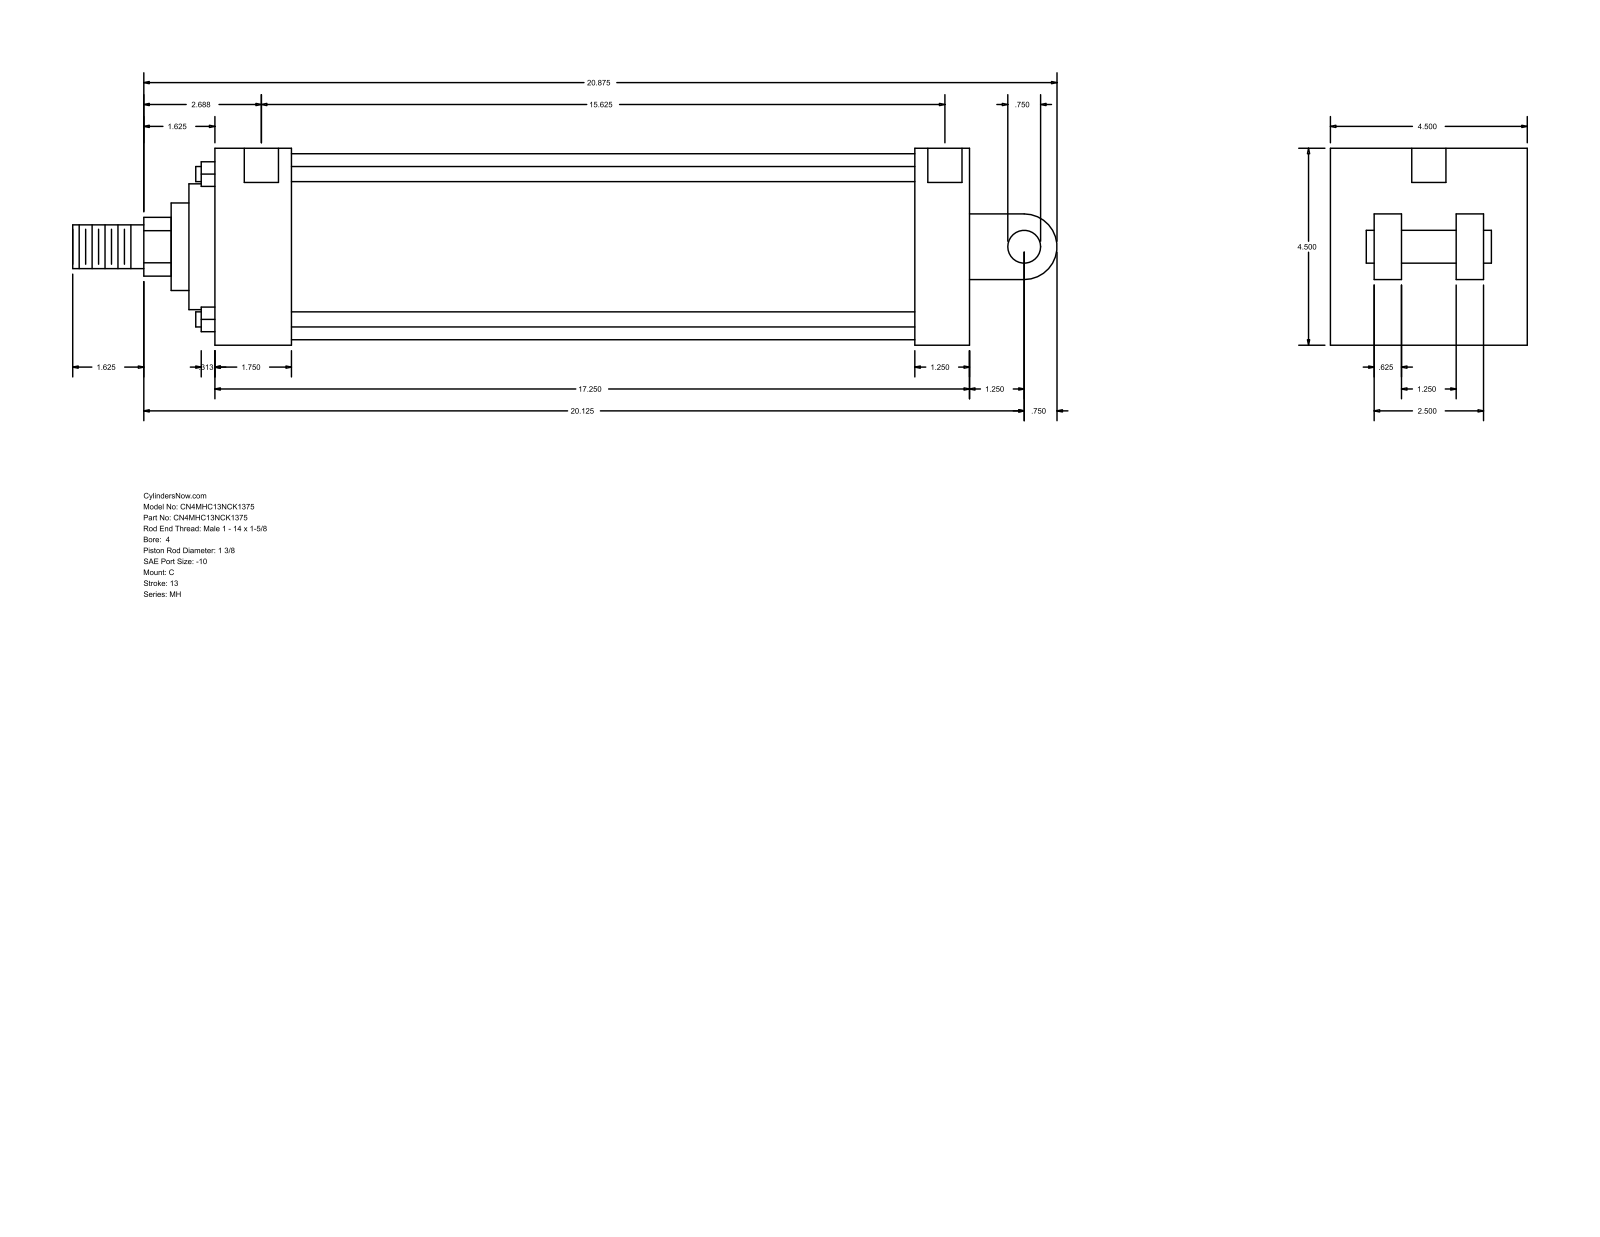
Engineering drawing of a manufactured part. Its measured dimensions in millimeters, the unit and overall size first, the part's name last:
Units: millimetres
Overall size (bounding box): 571.5 × 114.3 × 114.3
Round holes (diameter × count): ⌀8.73 ×4, ⌀19.84 ×2
Round bosses / shafts (diameter × count): ⌀8.76 ×4, ⌀107.95 ×1, ⌀73.03 ×1, ⌀50.8 ×1, ⌀34.92 ×1, ⌀25.4 ×1, ⌀19.05 ×1
Partial cylindrical surfaces — rounded edges, fillets, slot ends (radius × count): R17.06 ×1, R19.05 ×1
Main face-to-face distances: 114.3, 438.16, 44.45, 406.41, 361.96, 393.71, 31.75, 41.27, 73.03, 38.1
Hole centre spacings: 1.59, 398.47, 400.06, 396.88
Bodies: 0 solids, 101 faces (71 planar, 30 cylindrical, 0 other)
Part name (STEP PRODUCT): MH_C__0400_1.375
STEP written by: GSSL Pune (CONFIG_CONTROL_DESIGN)
